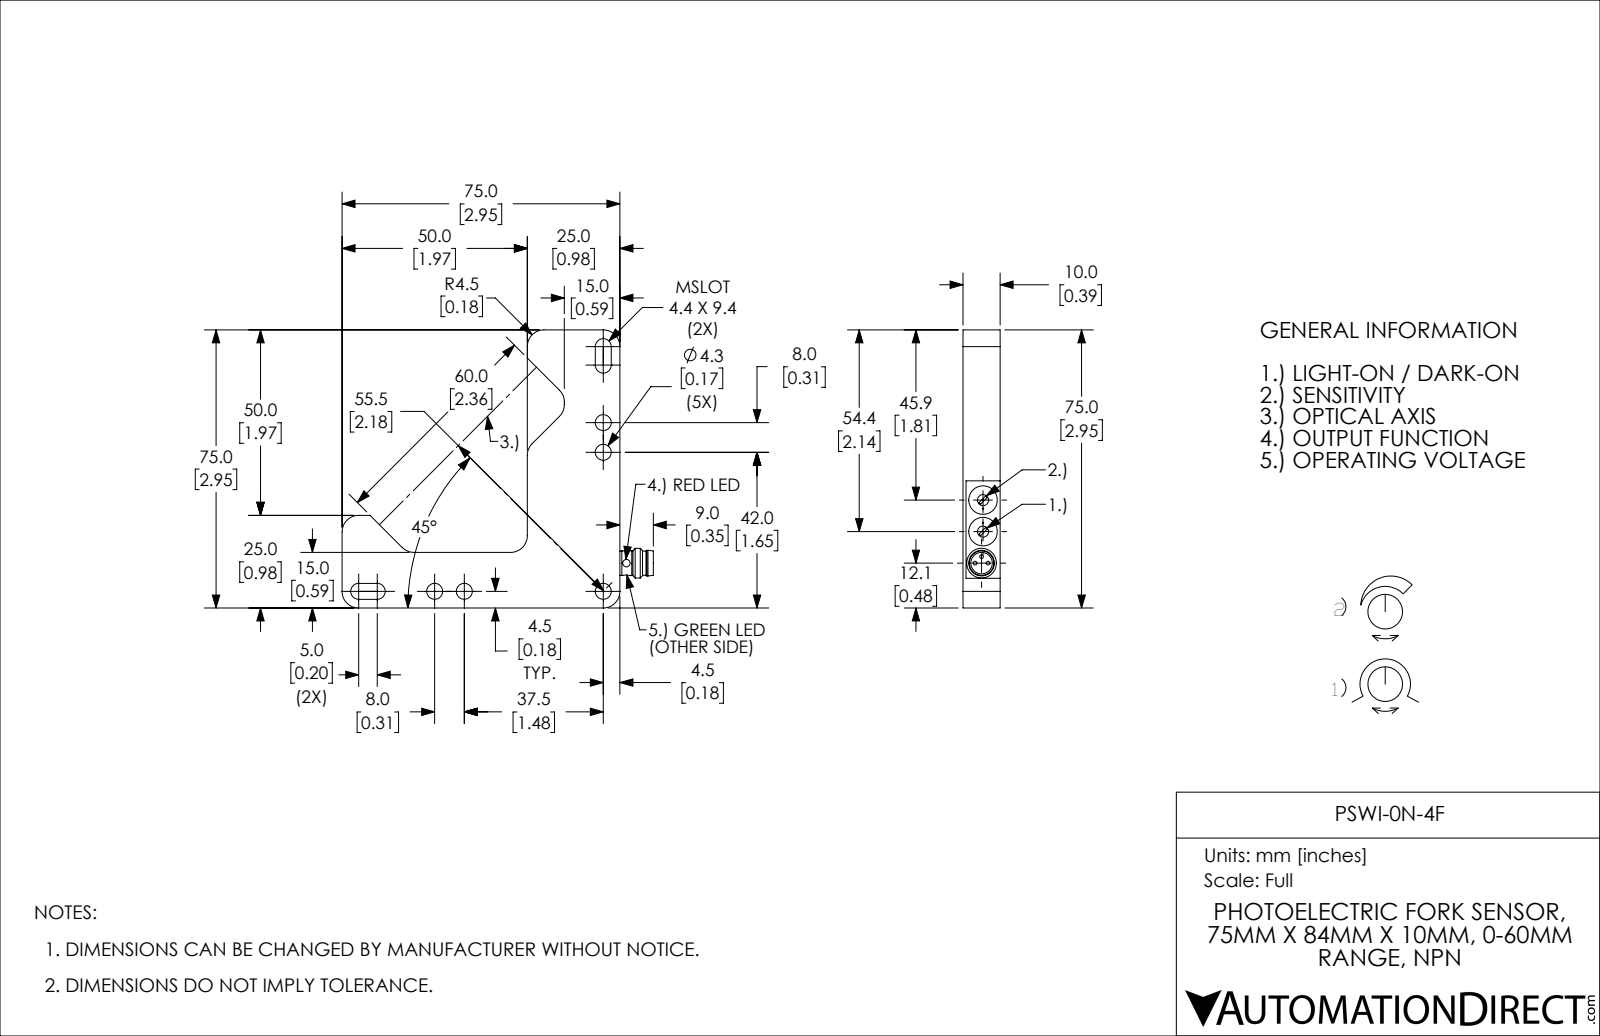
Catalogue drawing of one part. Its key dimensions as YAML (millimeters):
part_name: "PSWI-0N-4F"
step_written_by: "SolidWorks 2017 (AUTOMOTIVE_DESIGN)"
units: millimeters
bodies: {solids: 1, faces: 90, planar: 42, cylindrical: 41, other: 7}
overall_size: [84, 75, 10]
volume: 24650
surface_area: 9516
round_holes:
  - {diameter: 4.3, count: 5}
  - {diameter: 2, count: 2}
  - {diameter: 3, count: 2}
  - {diameter: 7.7, count: 2}
  - {diameter: 5.8, count: 1}
round_bosses_or_shafts:
  - {diameter: 1, count: 3}
  - {diameter: 8, count: 1}
  - {diameter: 6.9, count: 1}
  - {diameter: 6.7, count: 1}
  - {diameter: 6.5, count: 1}
partial_cylinders:
  - {radius: 4.5, count: 10}
  - {radius: 2.2, count: 4}
  - {radius: 1.2, count: 2}
face_to_face_distances: [10, 75, 60, 25, 15, 50, 74.9, 24.9, 6.7, 68.4]
hole_center_spacings: [8, 37.5, 45.5, 59, 8.5, 8.5, 9.8, 17]
